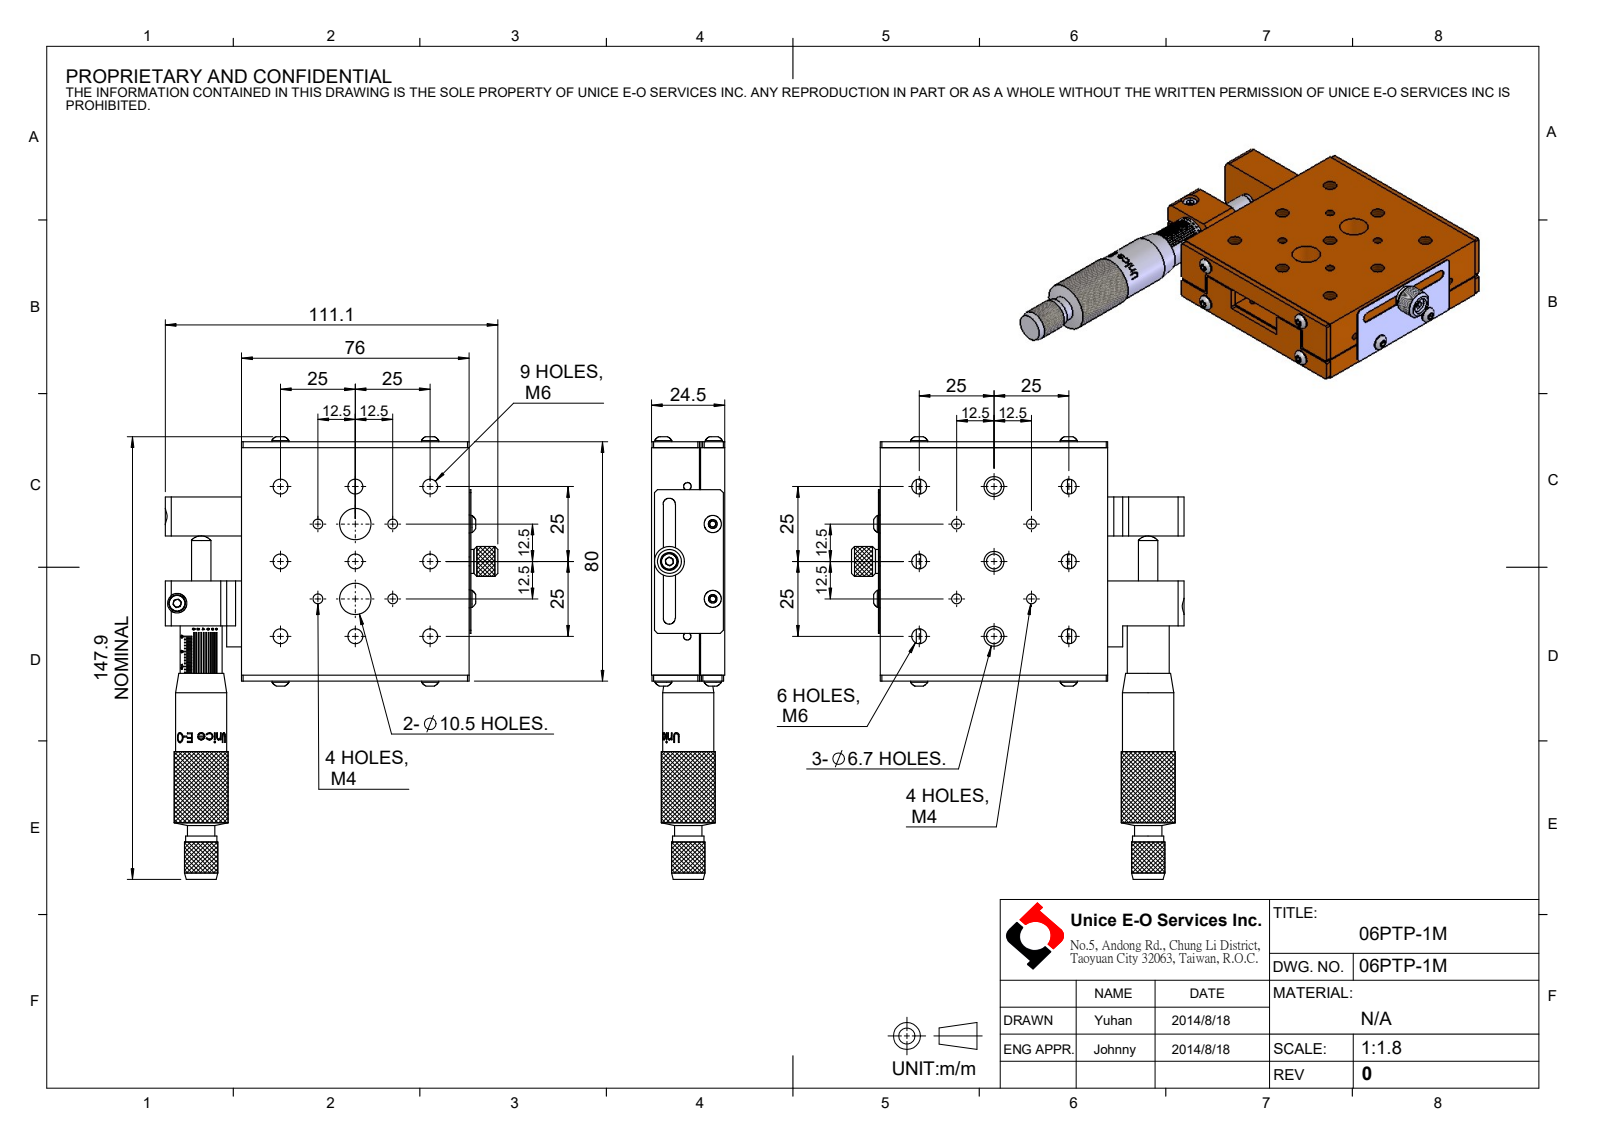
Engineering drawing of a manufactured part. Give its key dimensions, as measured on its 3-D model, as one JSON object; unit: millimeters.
{"part_name": "06PTP-1M", "step_written_by": "SolidWorks 2016 (CONFIG_CONTROL_DESIGN)", "units": "millimeters", "bodies": {"solids": 36, "faces": 2426, "planar": 903, "cylindrical": 654, "other": 869}, "overall_size": [135.35, 111.1, 24.5], "volume_mm3": 145171, "surface_area_mm2": 80209, "round_holes": [[2.5, 39], [3.5, 14], [6, 14], [3.3, 12], [4.5, 10], [5, 9], [3.4, 4], [6.5, 4], [6.7, 3], [3.2, 2], [10.5, 2], [3, 1]], "round_bosses_or_shafts": [[3, 12], [5.7, 8], [5.5, 5], [6, 2], [18.3, 1], [17.2, 1], [14, 1], [10, 1]], "partial_cylinders_radius": [[0.5, 32], [2, 8], [3, 2], [8.55, 1]], "face_to_face_distances": [8.2, 8, 8.3, 8.1, 16.4, 24.5, 16.5, 76, 7.9, 16.3], "hole_center_spacings": [25, 50, 17.68, 39.53, 10, 19.29, 20, 25.93]}
